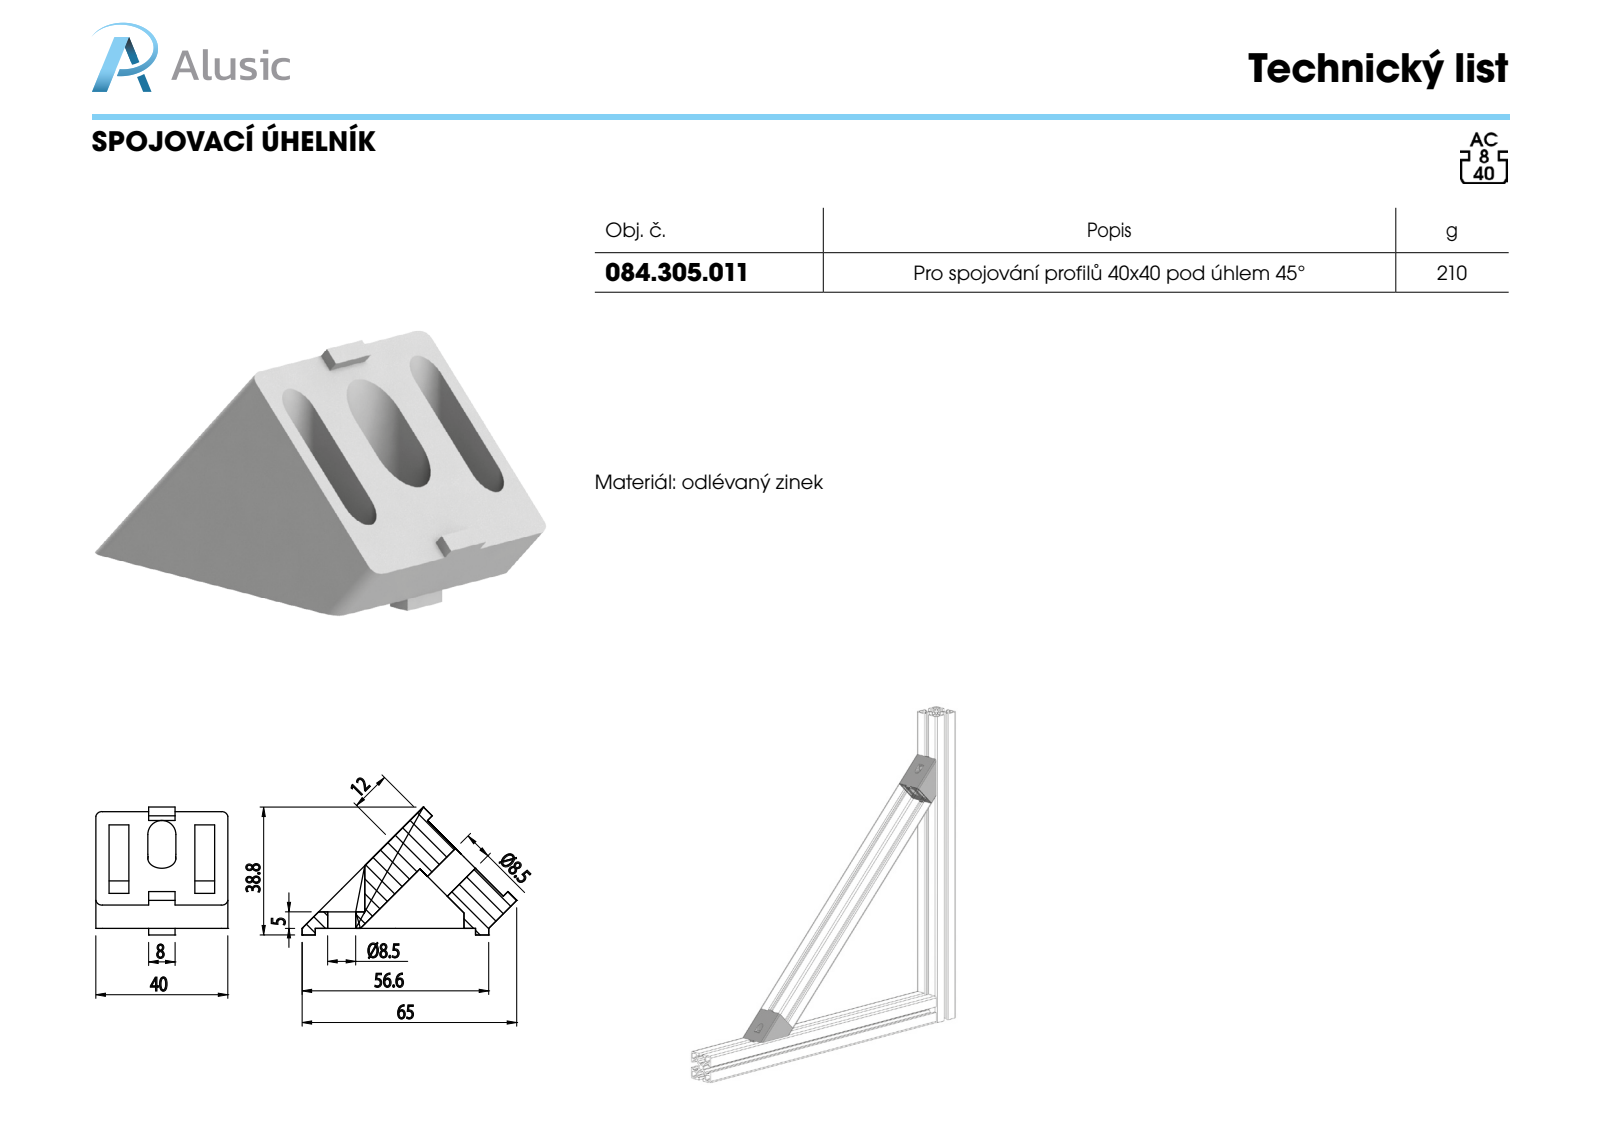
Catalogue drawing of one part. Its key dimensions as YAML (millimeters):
part_name: "084.305.011"
step_written_by: "SolidWorks 2016 (CONFIG_CONTROL_DESIGN)"
units: millimeters
bodies: {solids: 1, faces: 63, planar: 44, cylindrical: 19, other: 0}
overall_size: [63.64, 40, 37.35]
volume: 31952
surface_area: 13465
round_holes:
  - {diameter: 8.5, count: 2}
partial_cylinders:
  - {radius: 0.5, count: 4}
  - {radius: 2, count: 4}
  - {radius: 4.25, count: 2}
  - {radius: 7, count: 1}
  - {radius: 7.5, count: 1}
face_to_face_distances: [3, 6, 27, 1, 40, 9, 37, 31, 28, 5]
